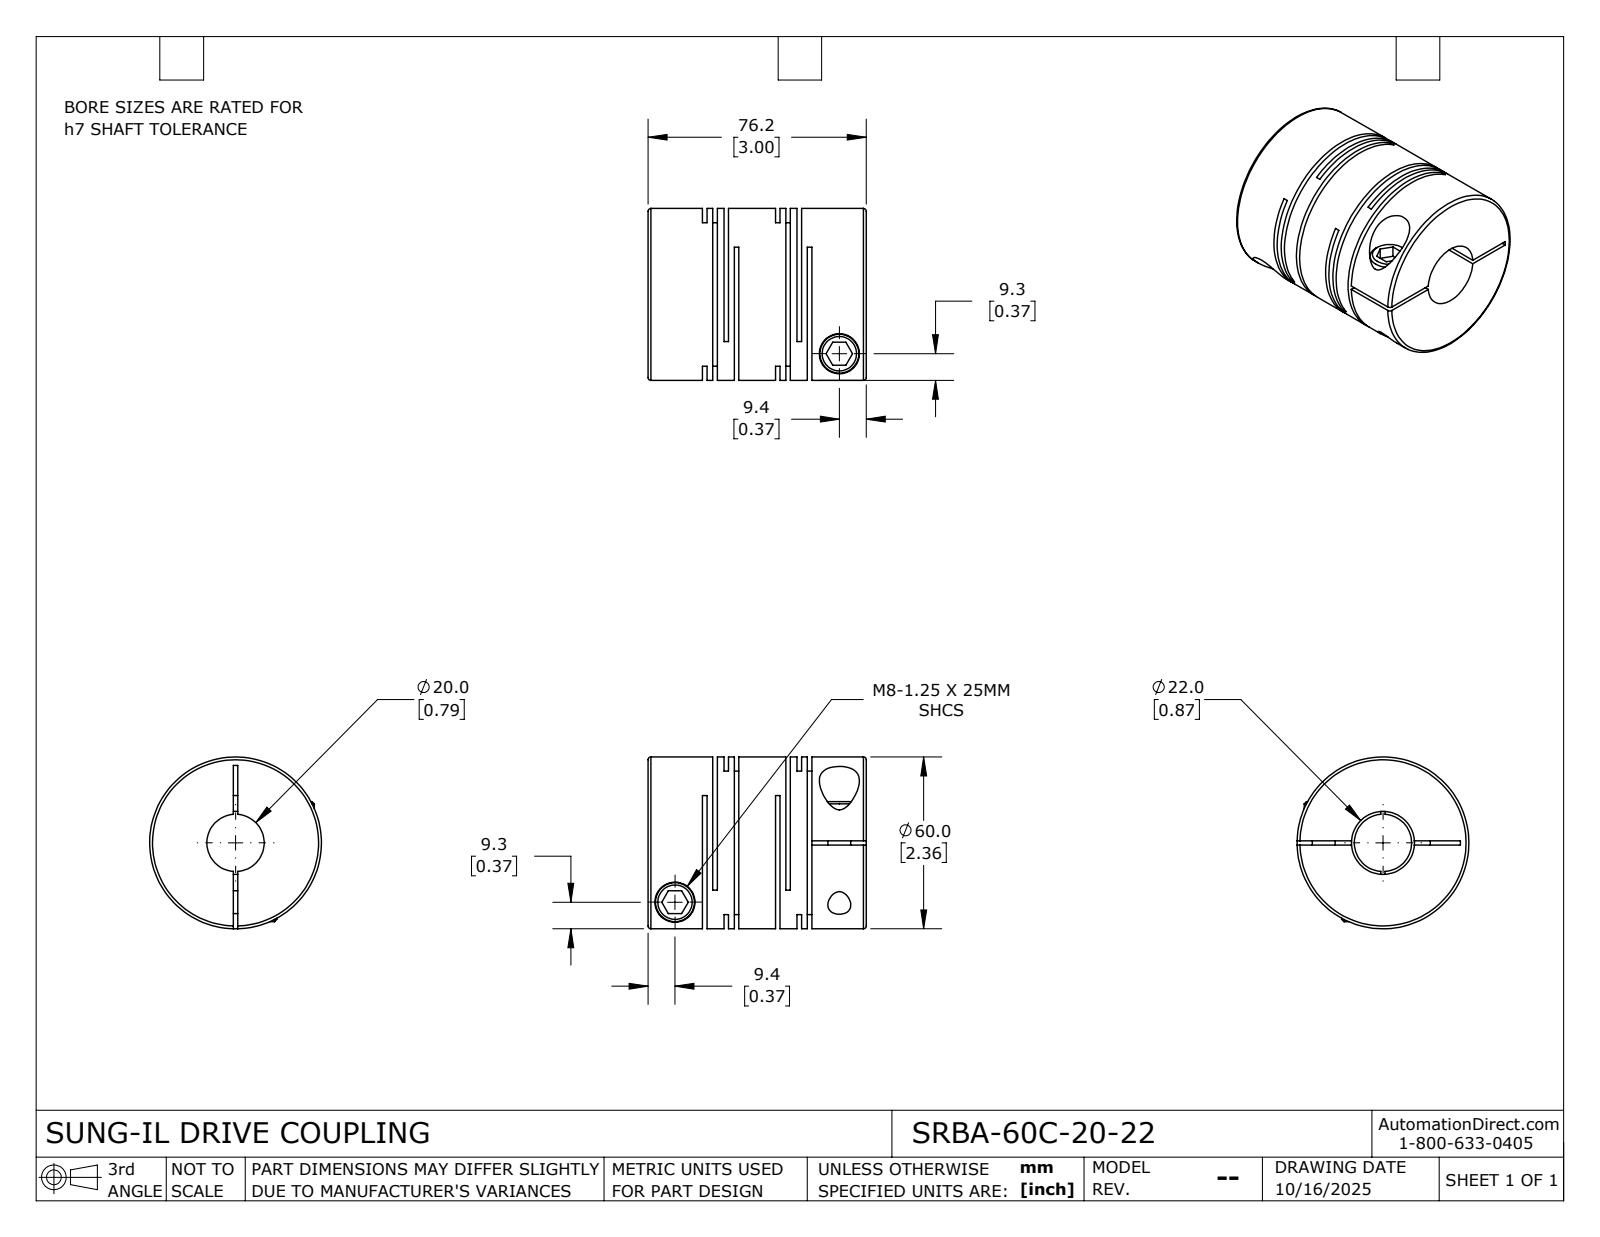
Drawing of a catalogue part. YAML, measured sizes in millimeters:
part_name: "SRBA-60C-20-22"
step_written_by: "SolidWorks 2024 (CONFIG_CONTROL_DESIGN)"
units: millimeters
bodies: {solids: 1, faces: 115, planar: 60, cylindrical: 42, other: 13}
overall_size: [76.2, 60, 60]
volume: 157406
surface_area: 58274
round_holes:
  - {diameter: 8, count: 2}
  - {diameter: 14, count: 2}
  - {diameter: 20, count: 1}
  - {diameter: 22, count: 1}
round_bosses_or_shafts:
  - {diameter: 13.6, count: 2}
  - {diameter: 60, count: 1}
face_to_face_distances: [1.6, 3.6, 7.5, 25.5, 33, 2, 5.9, 3.9, 23.9, 21.9]
